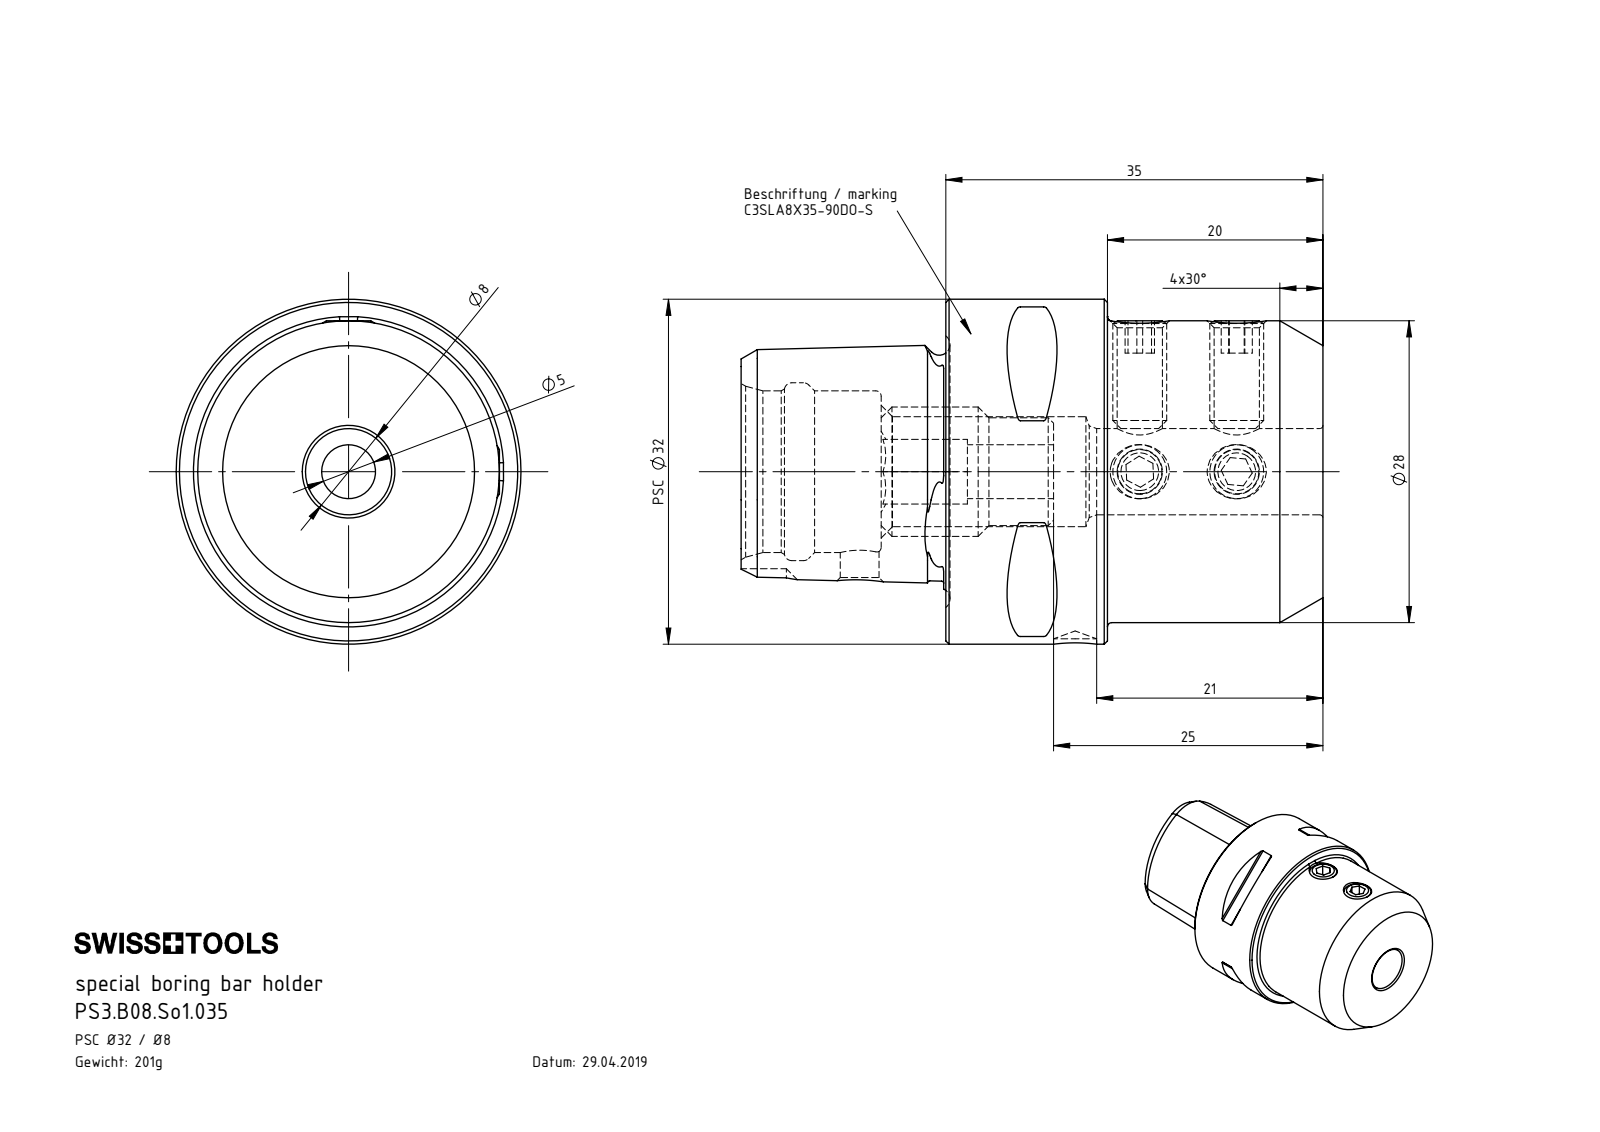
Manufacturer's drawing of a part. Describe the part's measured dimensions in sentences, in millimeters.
The part is named "ER1.PS3.012.016_A; ISO 4026 - M5 x 10_ISO 4026 - M5 x 10; ISO 4026 - M5 x 10; PS3-B08.So1.035_A (+1 more)". Its 3-D file was written by "SolidWorks 2017 (AUTOMOTIVE_DESIGN)". It is 6 solids with 236 faces: 65 planar, 49 cylindrical and 122 other. Overall it measures 54 by 32 by 32 millimeters. Its volume is 26 648 cubic millimeters and its surface area 9 898 square millimeters. Round holes: 4 of diameter 4.2, 1 of diameter 3.6, 1 of diameter 4, 1 of diameter 5, 1 of diameter 8, 1 of diameter 10.2, 1 of diameter 15, 1 of diameter 16.5. Round bosses or shafts: 4 of diameter 5, 1 of diameter 32, 1 of diameter 28, 1 of diameter 12, 1 of diameter 10. Partial cylindrical surfaces (rounded edges, fillets, slot ends): 8 of radius 0.3, 1 of radius 3. The main face-to-face distances are 35, 6, 15, 20, 19, 34, 54, 13, 21, 12.01. The hole center spacings are 9, 6, 15, 20, 26, 35.
